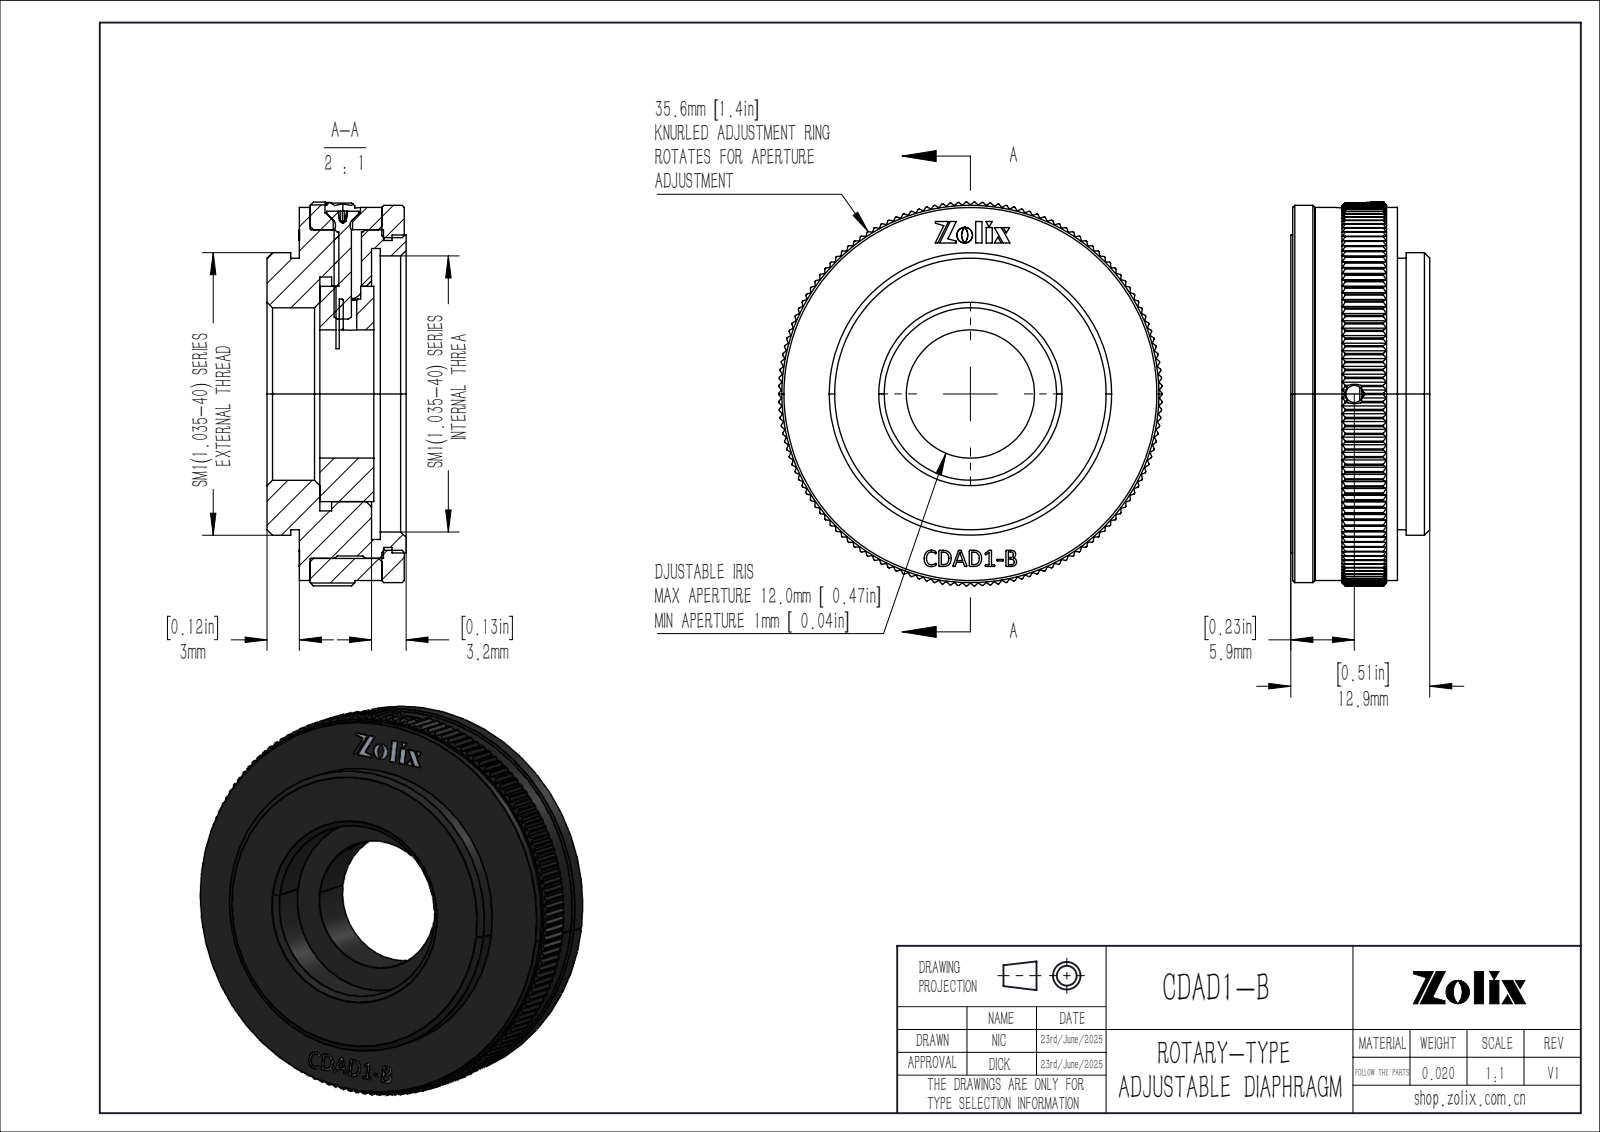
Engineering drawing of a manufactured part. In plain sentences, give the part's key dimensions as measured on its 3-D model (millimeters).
The part is named "CDAD1-B". Its 3-D file was written by "SolidWorks 2020 (CONFIG_CONTROL_DESIGN)". It is 5 solids with 900 faces: 590 planar, 209 cylindrical and 101 other. Overall it measures 35.6 by 35.59 by 12.9 millimeters. Its volume is 7 432 cubic millimeters and its surface area 7 956 square millimeters. Round holes: 1 of diameter 1.25, 1 of diameter 1.6, 1 of diameter 1.8, 1 of diameter 3.3, 1 of diameter 11.9, 1 of diameter 16, 1 of diameter 19.98, 1 of diameter 21.7, 1 of diameter 25.6, 1 of diameter 27, 1 of diameter 29, 1 of diameter 30.5. Round bosses or shafts: 1 of diameter 35, 1 of diameter 34.6, 1 of diameter 30.46, 1 of diameter 30.06, 1 of diameter 29.5, 1 of diameter 28.46, 1 of diameter 26.2, 1 of diameter 25.2. Partial cylindrical surfaces (rounded edges, fillets, slot ends): 2 of radius 1.05, 1 of radius 8.8, 1 of radius 17.8. The main face-to-face distances are 3, 0.9, 7.65, 1, 6.65, 1.9, 5.75, 3.03, 9.9, 6.7. The hole center spacings are 0.67.
